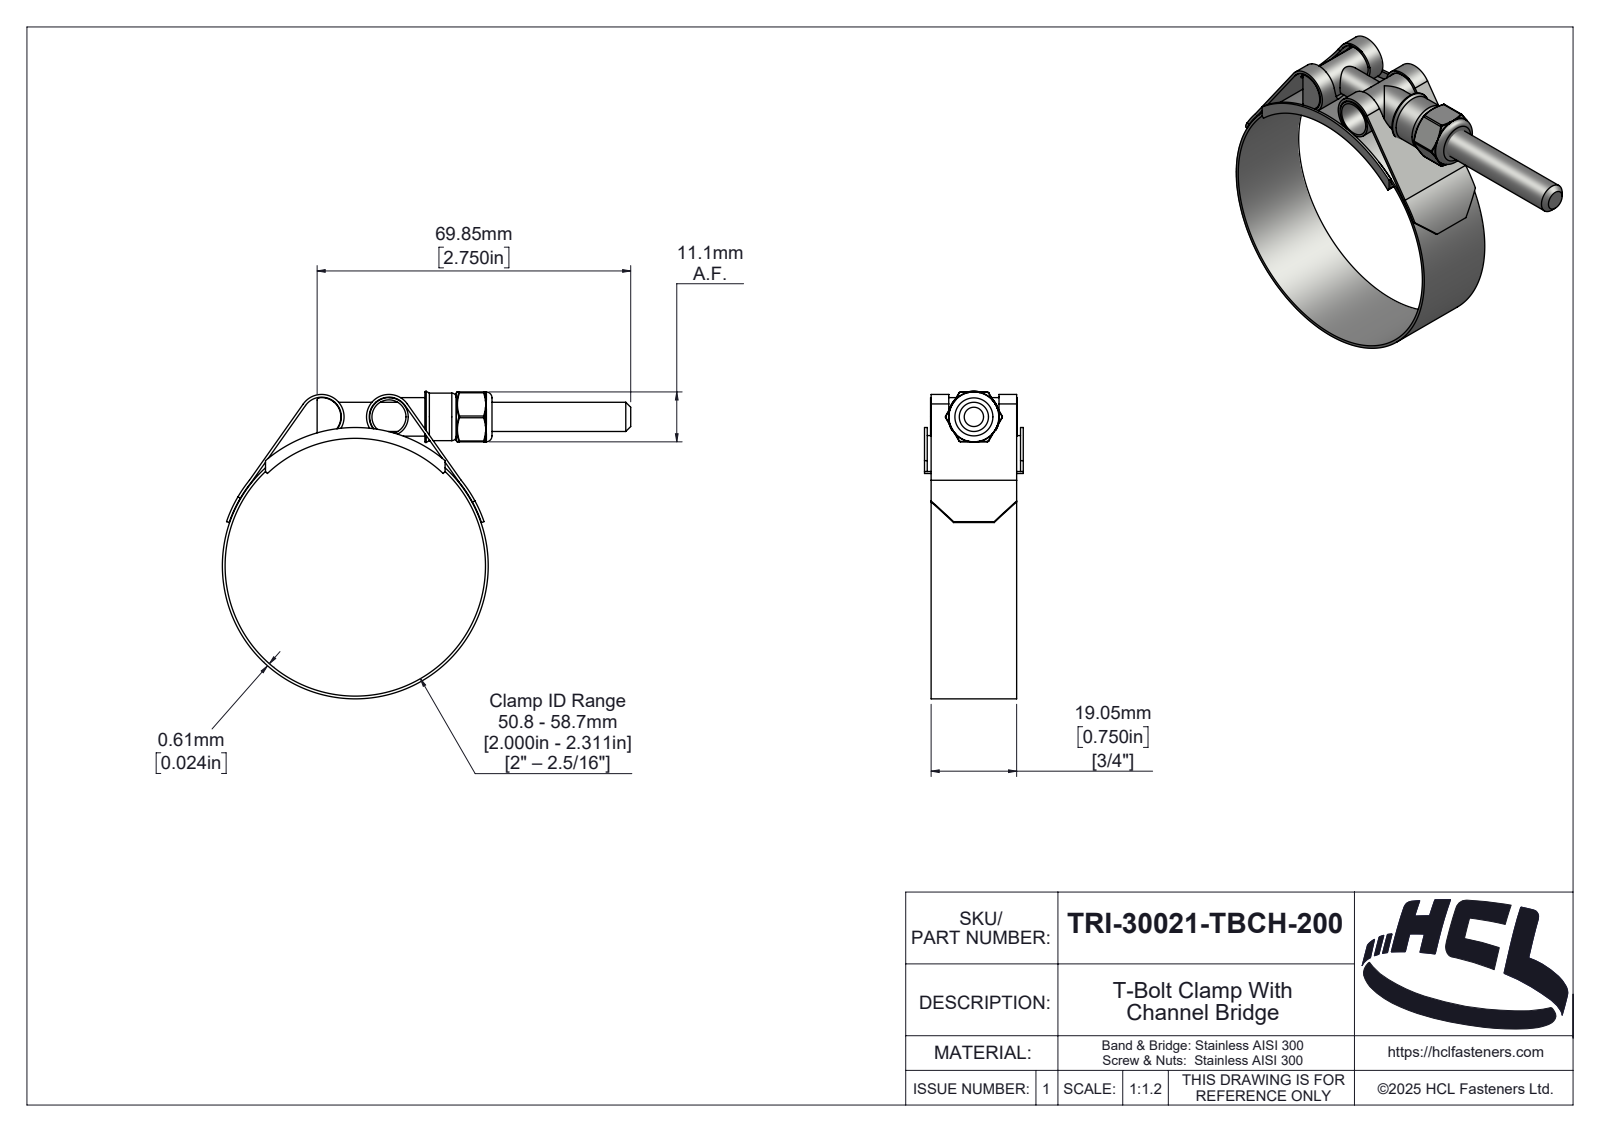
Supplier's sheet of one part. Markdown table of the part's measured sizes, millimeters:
| quantity | value |
| --- | --- |
| part name | TRI-30021-TBCH-200 |
| STEP written by | SolidWorks 2025 (AUTOMOTIVE_DESIGN) |
| units | millimeters |
| bodies | 6 solids, 334 faces (46 planar, 126 cylindrical, 162 other) |
| overall size | 90.96 × 68.49 × 22 |
| volume | 7 651 mm³ |
| surface area | 16 203 mm² |
| round holes (diameter × count) | 5.4 × 1, 6.35 × 1, 6.5 × 1, 7.58 × 1, 58 × 1 |
| round bosses / shafts (diameter × count) | 8.58 × 2, 59.22 × 1, 10.58 × 1 |
| partial cylindrical surfaces (radius × count) | 0.39 × 6, 0.5 × 2, 4.39 × 2, 5 × 2, 5.6 × 2, 0.59 × 1, 2.42 × 1, 3.03 × 1 |
| main face-to-face distances | 0.61, 1.47, 20.53, 19.06, 21.39, 0.86, 19.92, 0.74, 11.11, 22 |
| hole center spacings | 34 |
